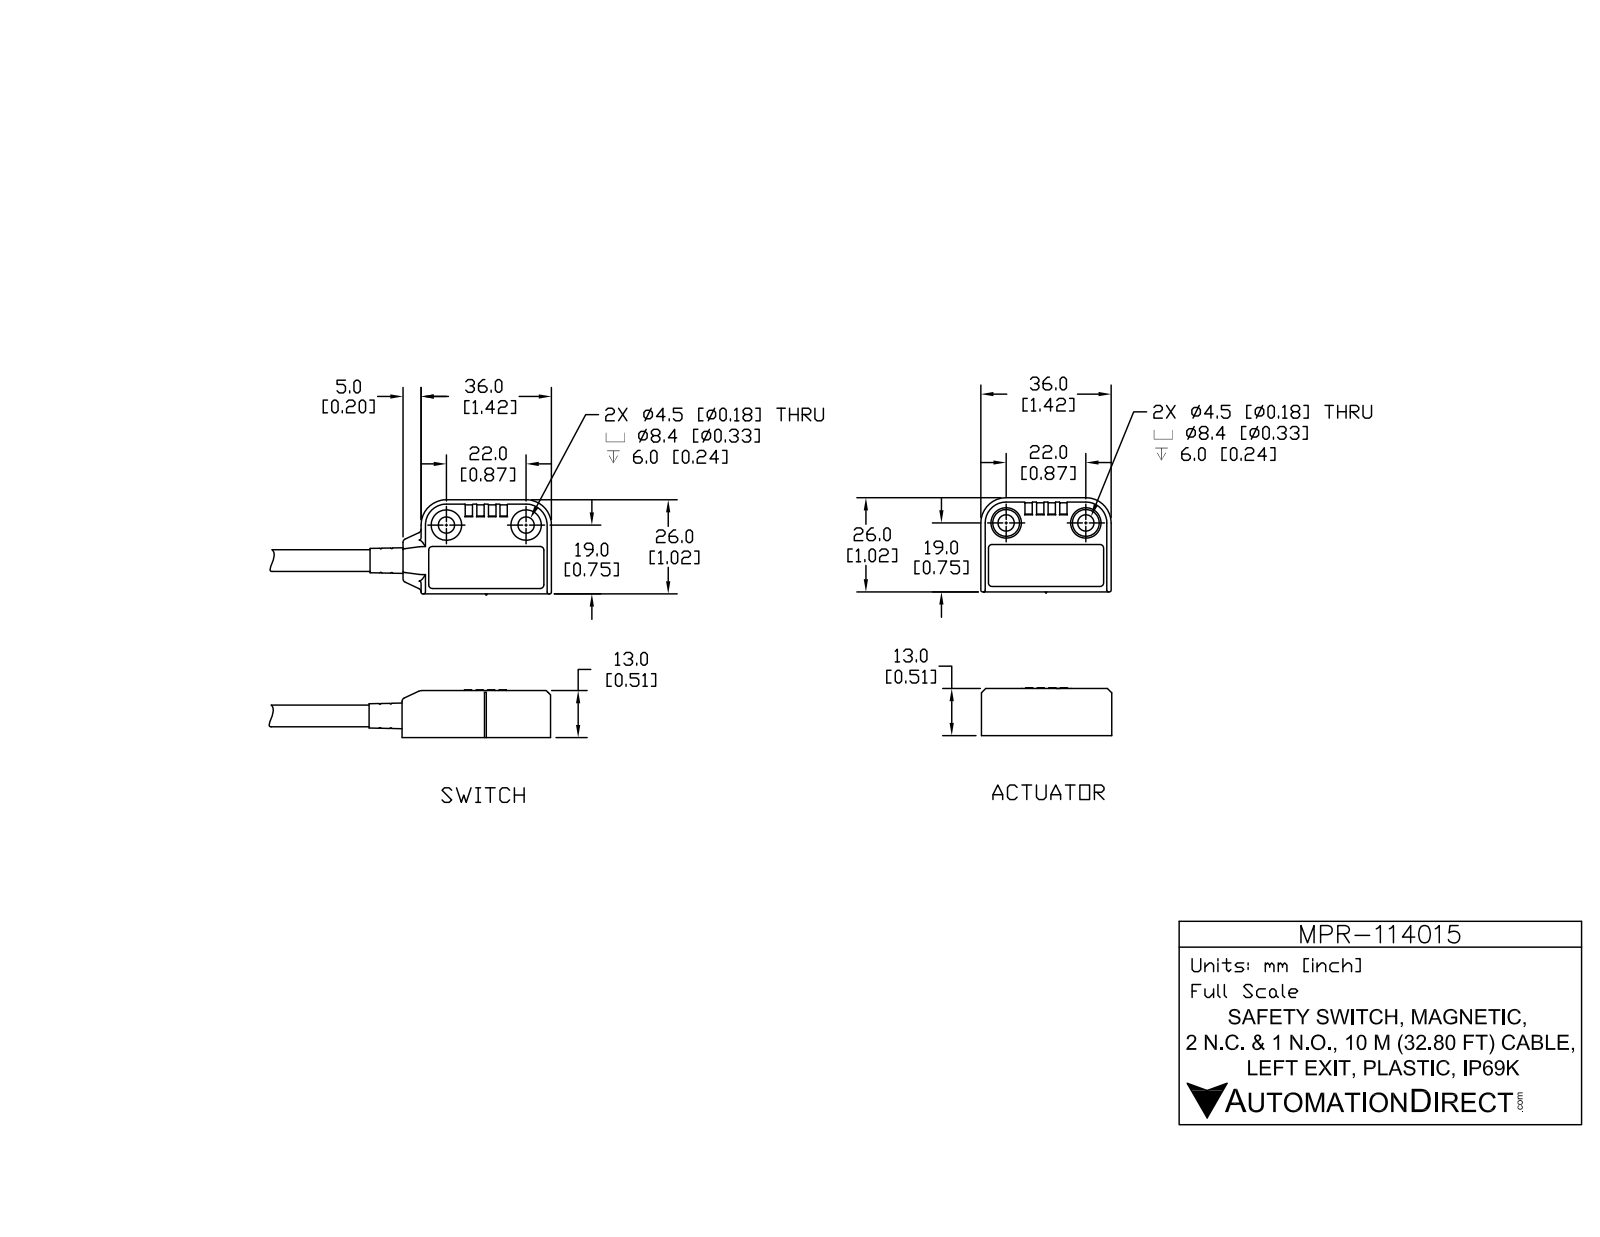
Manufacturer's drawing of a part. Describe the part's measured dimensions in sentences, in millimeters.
The part is named "MPR-114015; MPR-114015_2; MPR-114015_1". Its 3-D file was written by "SolidWorks 2017 (AUTOMOTIVE_DESIGN)". It is 9 solids with 1116 faces: 493 planar, 327 cylindrical and 296 other. Overall it measures 194.5 by 53 by 13.4 millimeters. Its volume is 17 350 cubic millimeters and its surface area 19 080 square millimeters. Round holes: 4 of diameter 4.5, 4 of diameter 8.4, 2 of diameter 5, 1 of diameter 5, 1 of diameter 5.9, 1 of diameter 7. Round bosses or shafts: 3 of diameter 2, 2 of diameter 5, 2 of diameter 2.3, 1 of diameter 8.6, 1 of diameter 7.6, 1 of diameter 7.1, 1 of diameter 6. Partial cylindrical surfaces (rounded edges, fillets, slot ends): 85 of radius 0.5, 30 of radius 0.2, 28 of radius 0.3, 17 of radius 0.1, 13 of radius 1, 4 of radius 4.3, 4 of radius 5.1, 4 of radius 7. The main face-to-face distances are 1.4, 11.7, 9.9, 11.5, 1.2, 27, 1.5, 2.4, 11.3, 0.8. The hole center spacings are 22, 11.3, 24.7, 27.7, 35.4, 39, 44.8, 10.1.
